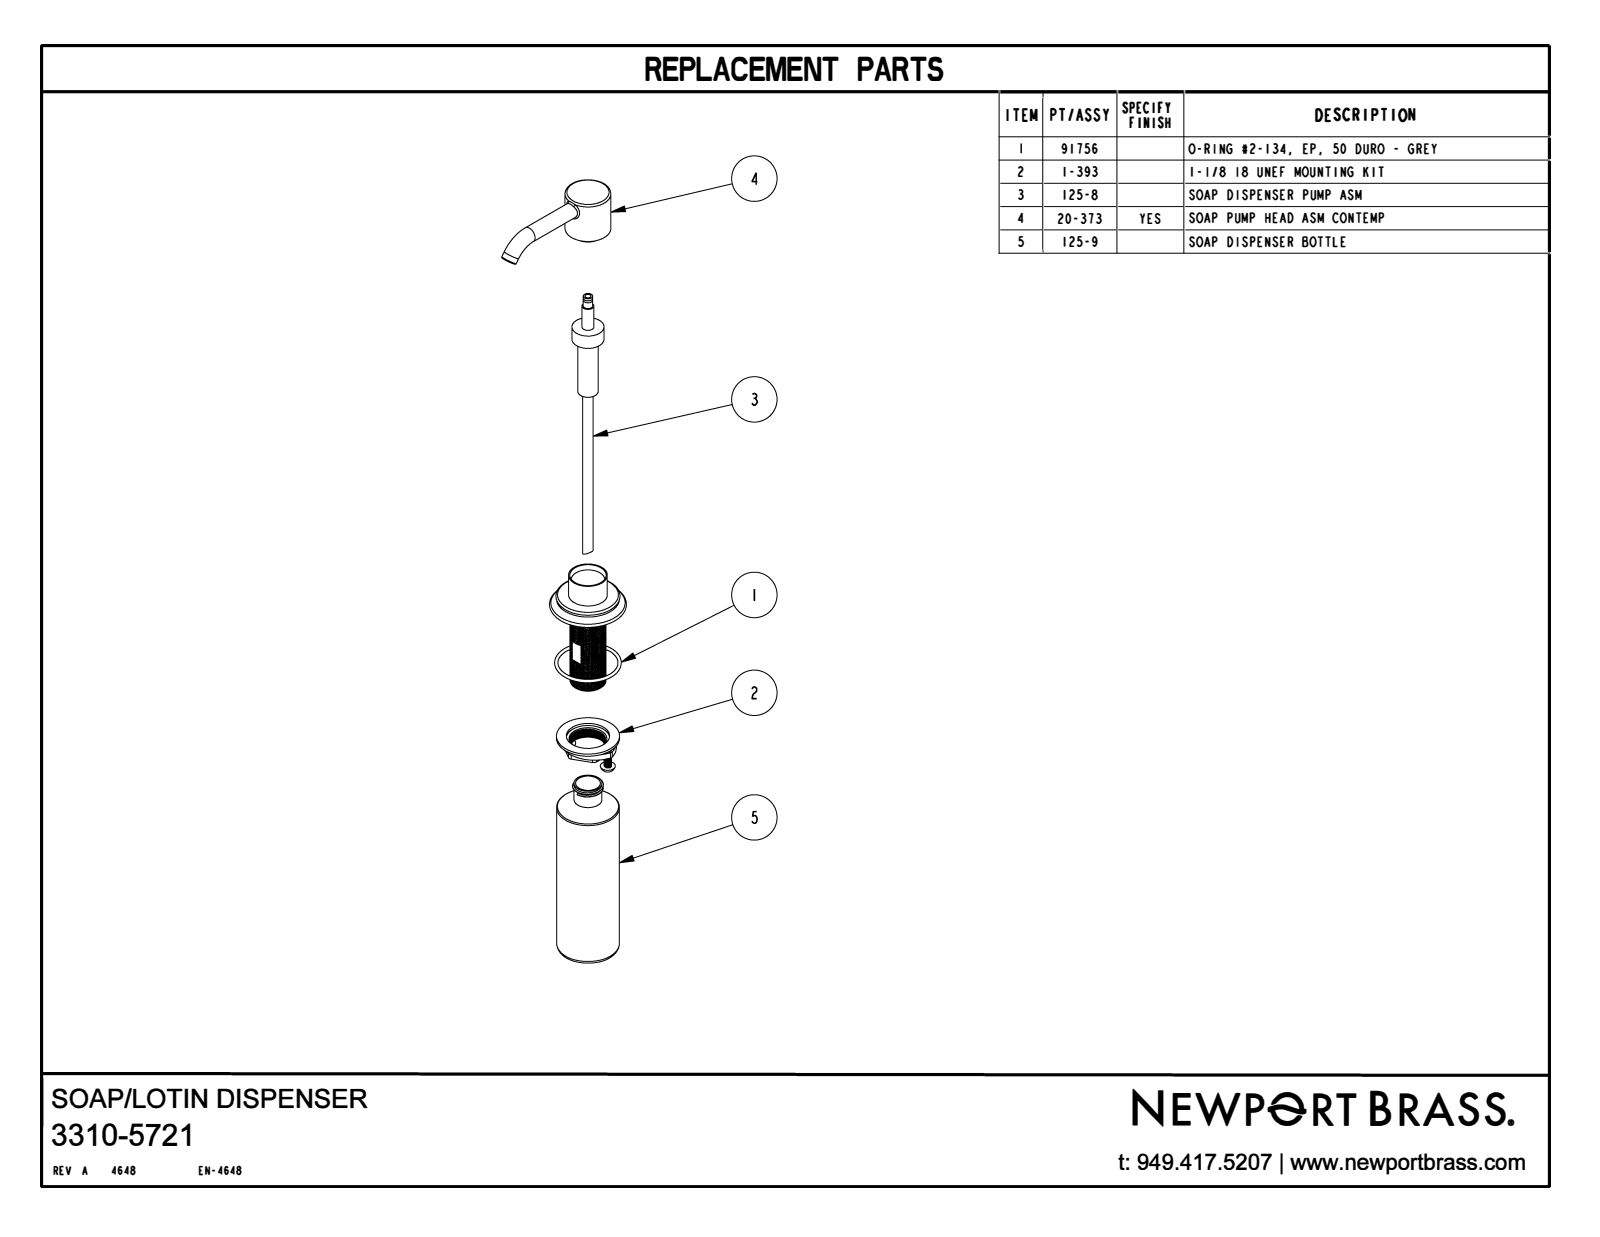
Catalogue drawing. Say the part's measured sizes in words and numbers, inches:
The part is named "3310-5721". Its 3-D file was written by "CREO PARAMETRIC BY PTC INC, 2018400 (CONFIG_CONTROL_DESIGN)". It is 1 solid with 40 faces: 6 planar, 12 cylindrical and 22 other. Overall it measures 4.886 by 2.416 by 2.4 inches. Its volume is 5.01 cubic inches and its surface area 24.97 square inches. Round holes: 1 of diameter 0.35. Round bosses or shafts: 2 of diameter 0.5, 1 of diameter 1.43, 1 of diameter 1.21, 1 of diameter 0.335. The main face-to-face distances are 0.425, 1.021, 0.596, 0.02, 0.05, 0.03.
